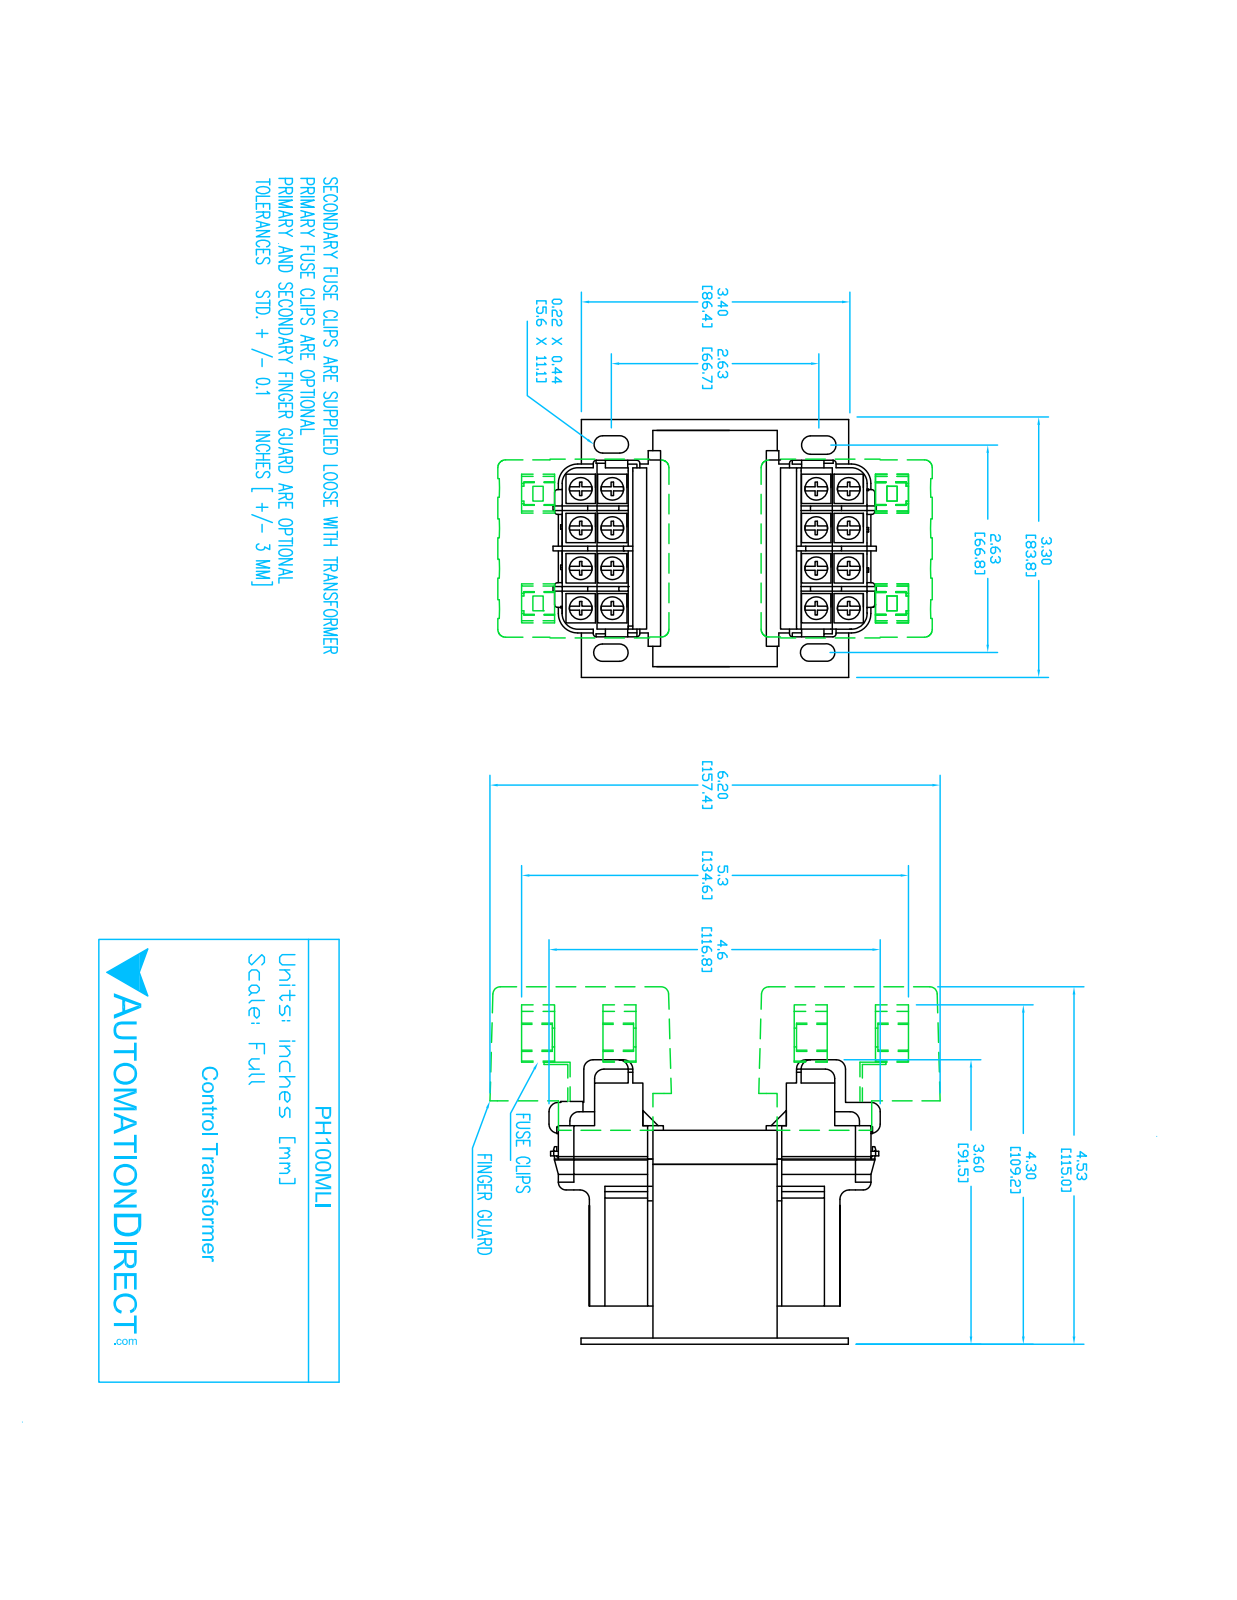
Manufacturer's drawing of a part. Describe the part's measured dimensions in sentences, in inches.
The part is named "PH100MLI". Its 3-D file was written by "SolidWorks 2017 (AUTOMOTIVE_DESIGN)". It is 8 solids with 500 faces: 292 planar, 148 cylindrical and 60 other. Overall it measures 4.567 by 3.514 by 3.25 inches. Its volume is 29.38 cubic inches and its surface area 125.8 square inches. Round holes: 4 of diameter 0.157. Partial cylindrical surfaces (rounded edges, fillets, slot ends): 46 of radius 0.039, 28 of radius 0.079, 8 of radius 0.11, 8 of radius 0.197, 4 of radius 0.118, 4 of radius 0.246. The main face-to-face distances are 2.136, 1.969, 0.136, 0.364, 2, 0.398, 2.602, 2.5, 0.118, 0.5. The hole center spacings are 1.128, 2.624, 2.857.
